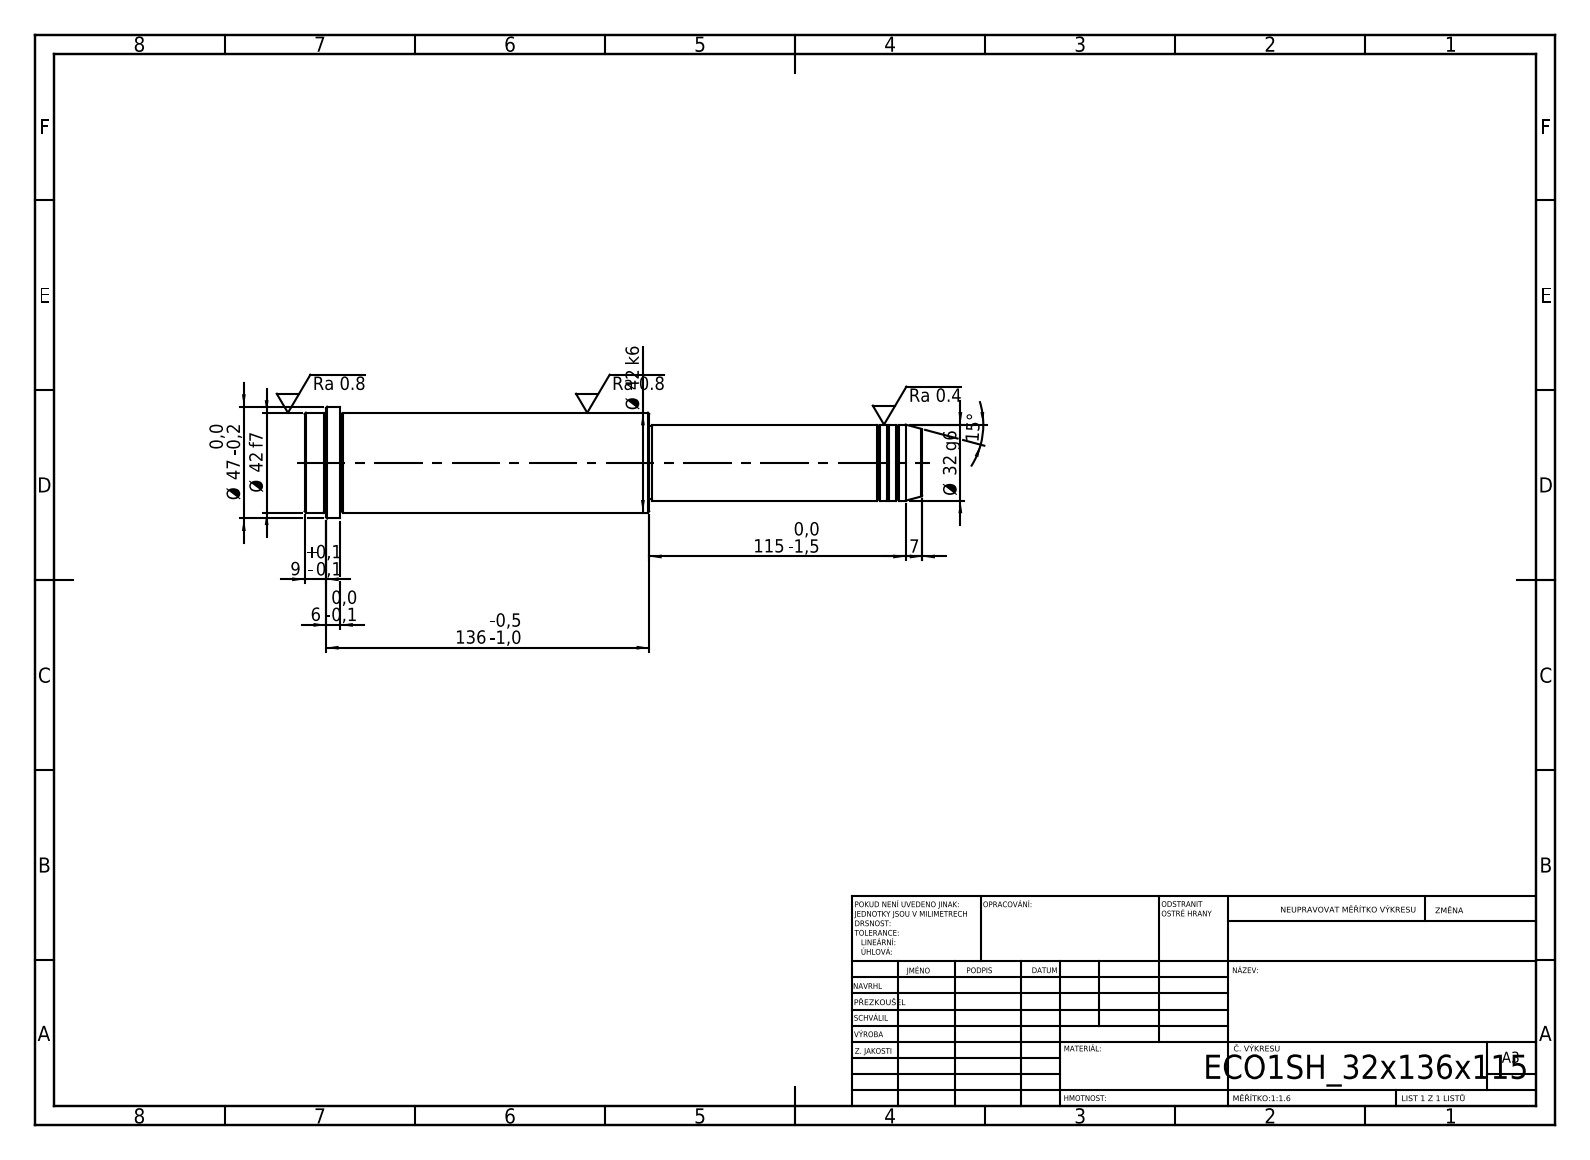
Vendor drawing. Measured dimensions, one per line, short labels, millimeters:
written by: SolidWorks 2019 (CONFIG_CONTROL_DESIGN)
unit: mm
bodies: 1 solid, 52 faces (6 planar, 16 cylindrical, 30 other)
size: 260 × 47 × 47
volume: 294 518 mm³; area: 34 333 mm²
bosses: 1× ⌀47, 1× ⌀42, 1× ⌀32, 1× ⌀31
face distances: 260, 115, 145, 245, 130, 15, 251, 136, 6, 9
